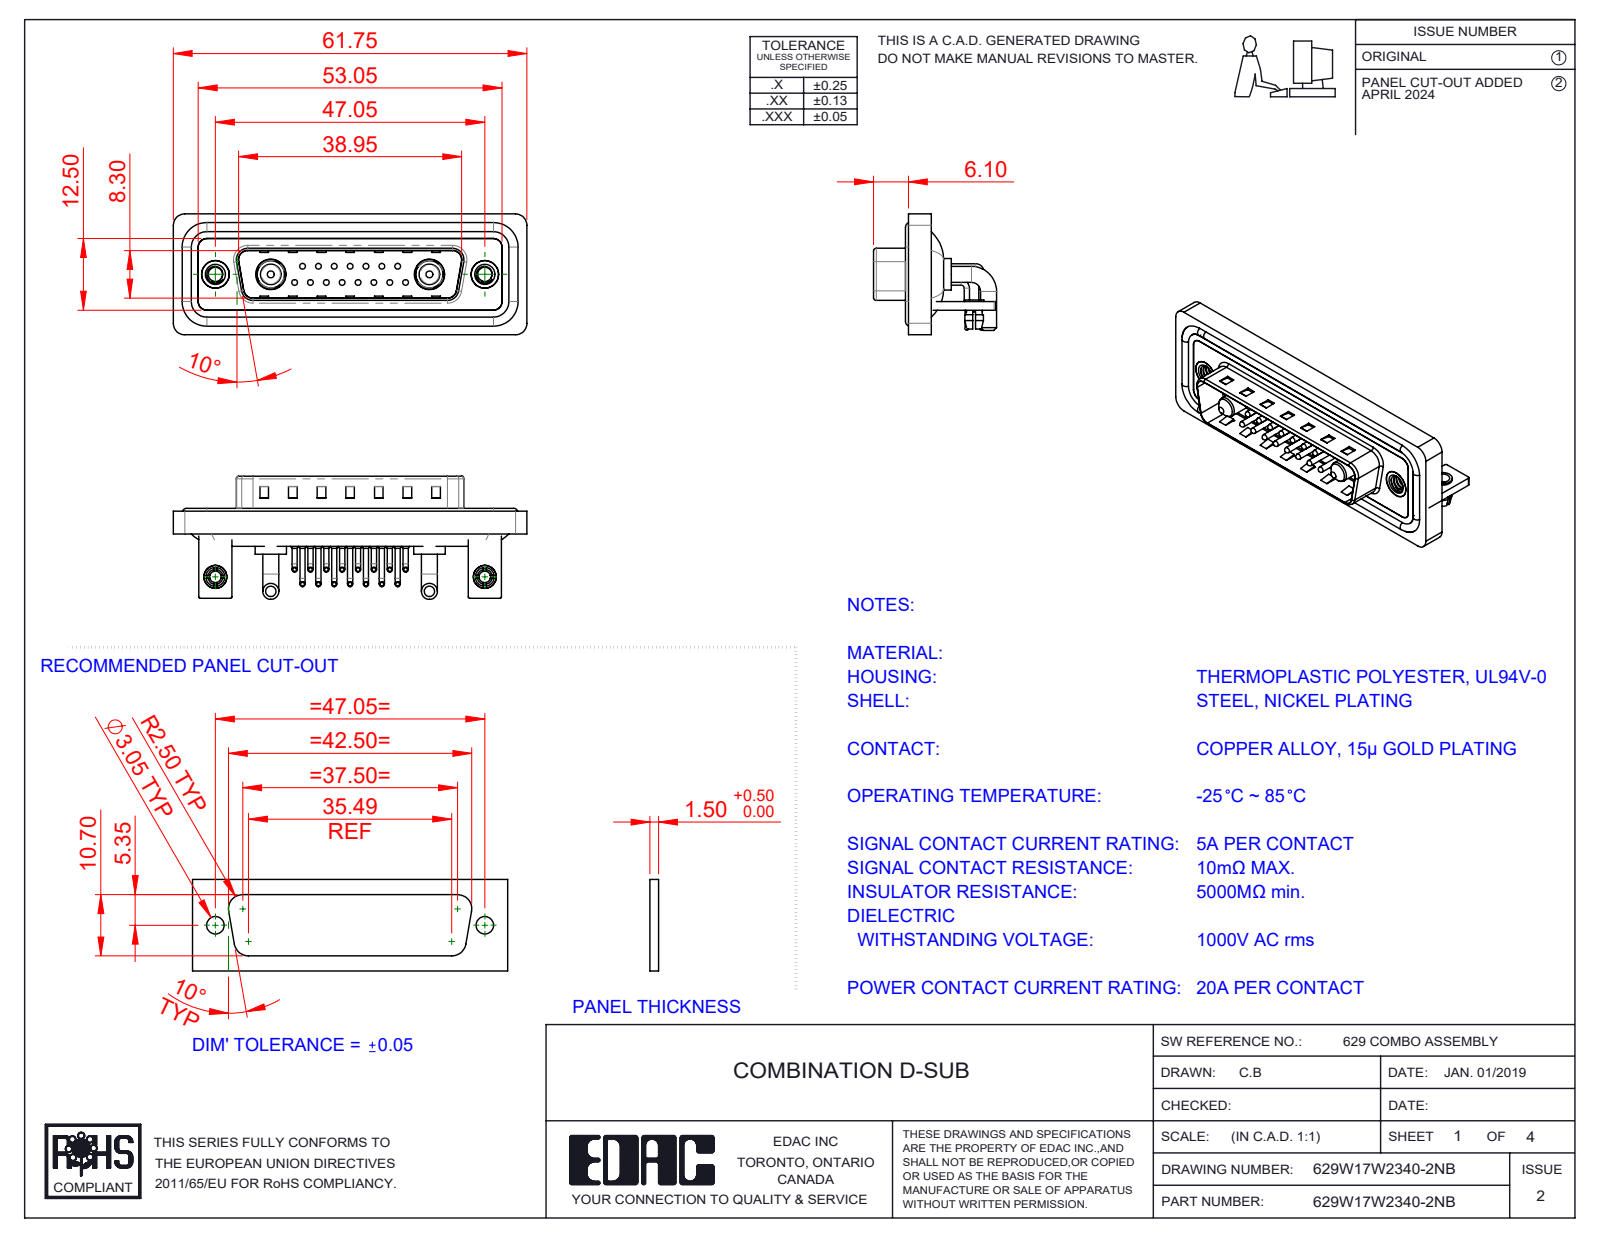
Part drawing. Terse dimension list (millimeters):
name: 629Combo Contact Row 1; 629Combo Waterproof Housing_25 Contacts; 629Combo Stabilizer Bracket; 629W17W2340-2NB (+7 more)
written by: SolidWorks 2023 (CONFIG_CONTROL_DESIGN)
unit: mm
bodies: 30 solids, 2349 faces (1257 planar, 820 cylindrical, 272 other)
size: 61.75 × 21.5 × 21.1
volume: 7 820 mm³; area: 13 399 mm²
holes: 17× ⌀2, 15× ⌀0.75, 15× ⌀1.6, 4× ⌀2.5, 2× ⌀3.2, 2× ⌀4, 2× ⌀4.8, 2× ⌀4.85, 2× ⌀5, 2× ⌀5.3
bosses: 30× ⌀0.9, 15× ⌀1.5, 15× ⌀1, 15× ⌀0.65, 4× ⌀2.8, 4× ⌀1.6, 2× ⌀5.5, 2× ⌀5.2
rounds: 19× R2, 18× R1.5, 16× R0.25, 15× R1.01, 9× R0.5, 8× R1.6, 4× R0.6, 4× R0.65
face distances: 0.4, 0.8, 1.5, 2.1, 2.9, 1.1, 4.1, 1.6, 4.5, 3.7
hole spacings: 3.16, 2.77, 5.54, 8.31, 5.04, 7.49, 11.08, 5.03
